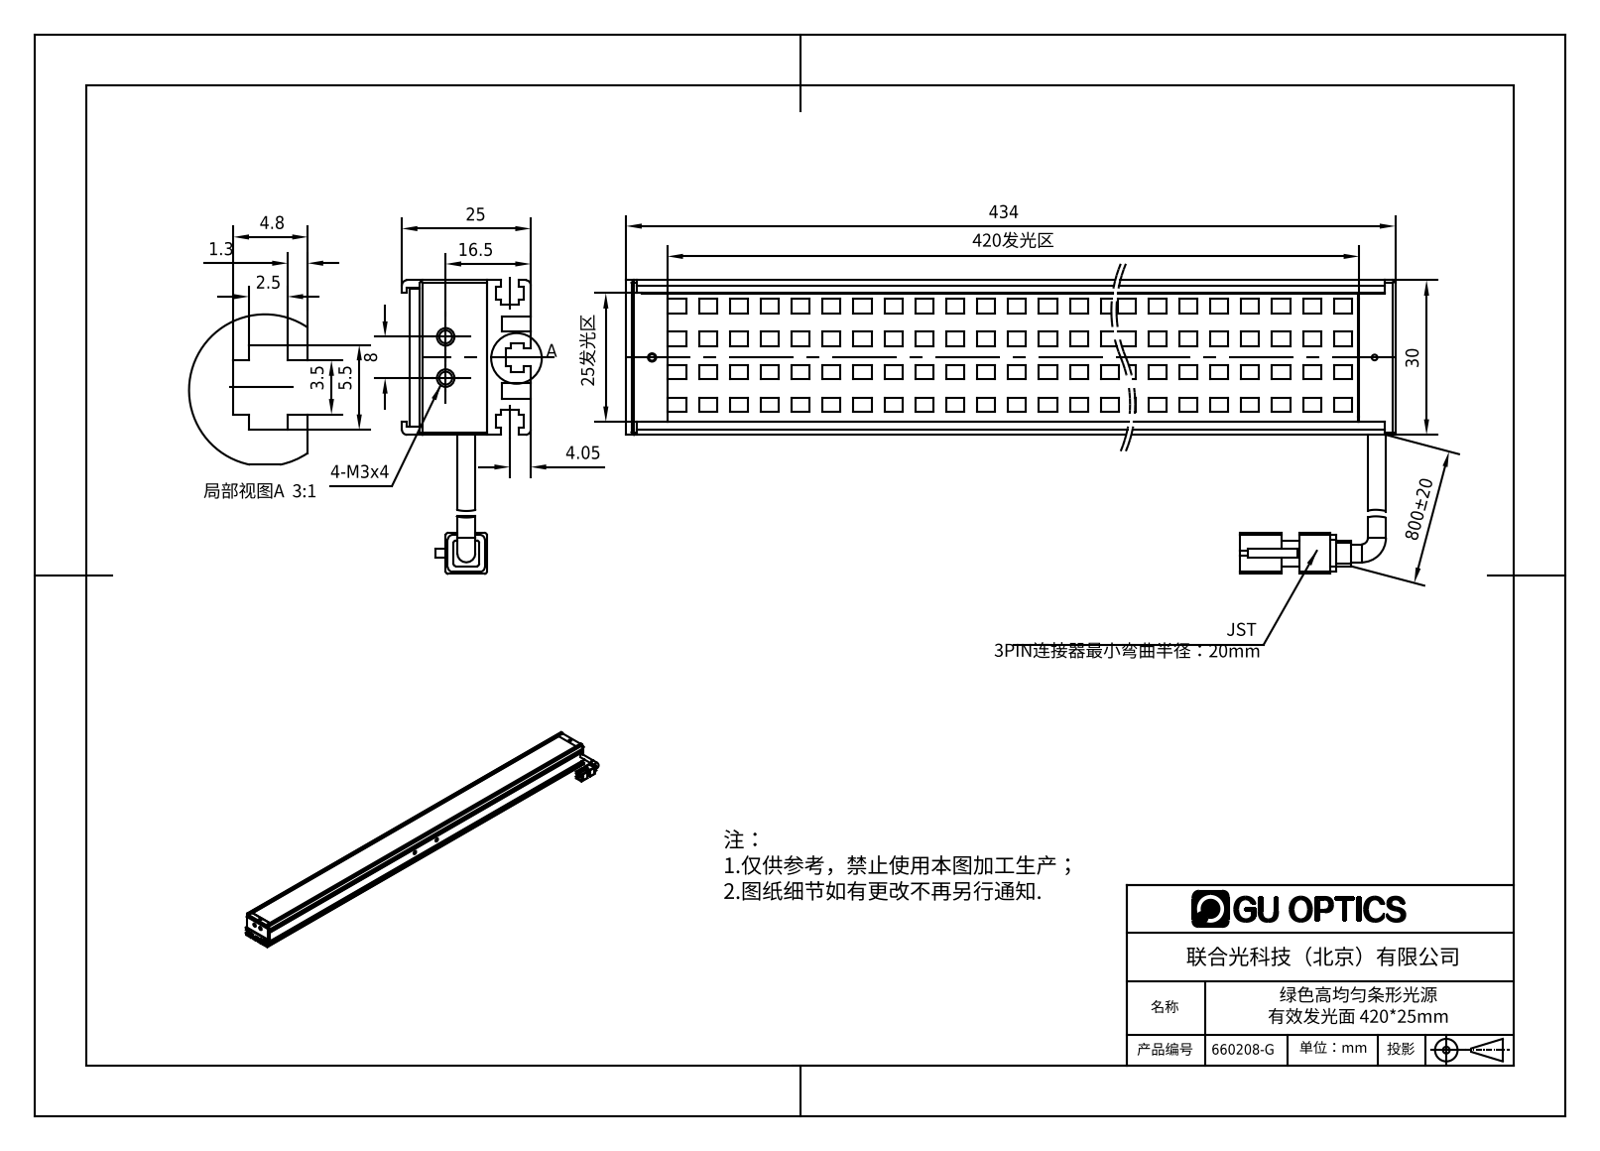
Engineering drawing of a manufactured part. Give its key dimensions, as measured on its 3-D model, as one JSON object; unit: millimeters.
{"part_name": "660208-G", "step_written_by": "SolidWorks 2016 (AUTOMOTIVE_DESIGN)", "units": "millimeters", "bodies": {"solids": 6, "faces": 1842, "planar": 1656, "cylindrical": 83, "other": 103}, "overall_size": [434, 57, 25], "volume_mm3": 145249, "surface_area_mm2": 148514, "round_holes": [[1.6, 5], [1.5, 2], [1.7, 2], [2.5, 2], [2.8, 2], [3, 2], [1.1, 1], [1.25, 1], [2, 1]], "round_bosses_or_shafts": [[3.5, 2]], "partial_cylinders_radius": [[1, 12], [0.5, 8], [1.65, 1]], "face_to_face_distances": [1, 2, 13, 2.5, 3, 27.5, 9.5, 4.5, 12, 15.1], "hole_center_spacings": [425, 7, 425.06, 8, 30, 197, 197.11, 198]}
